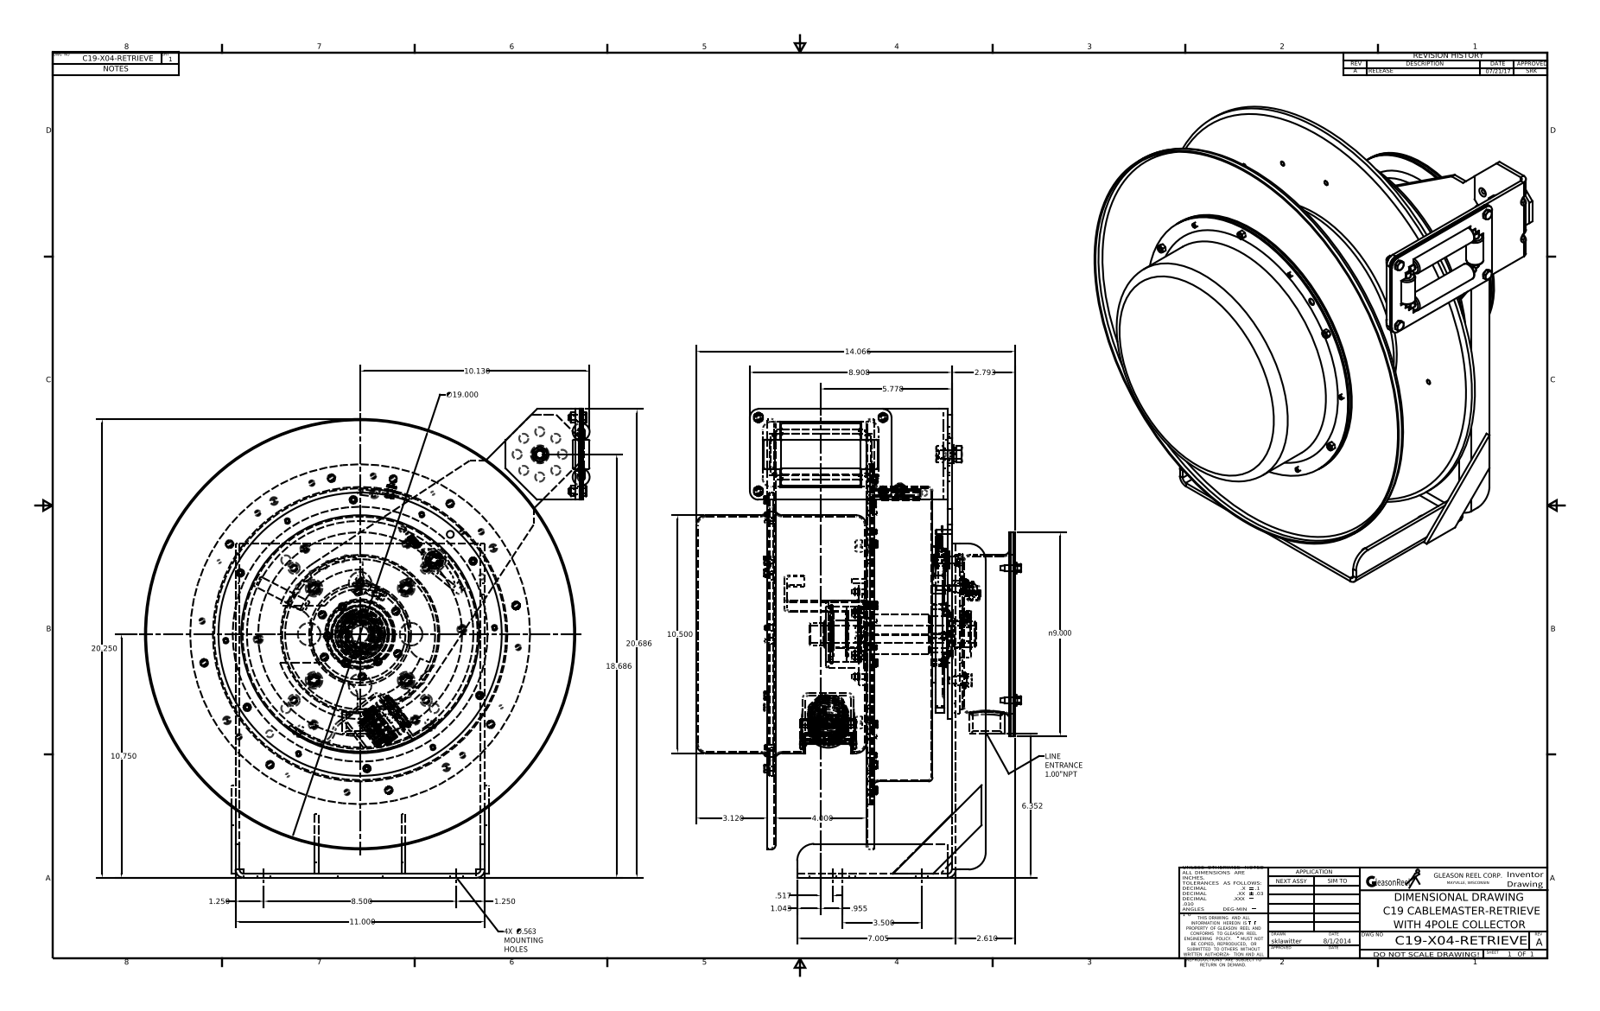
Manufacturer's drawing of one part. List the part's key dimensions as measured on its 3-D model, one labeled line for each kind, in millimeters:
Part name (STEP PRODUCT): C19-X04-RETRIEVE (SW)
STEP written by: Autodesk Inventor 2016 (AUTOMOTIVE_DESIGN)
Units: millimetres
Bodies: 173 solids, 3480 faces (1373 planar, 1017 cylindrical, 1090 other)
Overall size (bounding box): 525.44 × 498.61 × 363.98
Volume: 3 830 000 mm³ · Surface area: 3 140 000 mm²
Round holes (diameter × count): ⌀6.35 ×39, ⌀5 ×30, ⌀4.13 ×26, ⌀5.56 ×14, ⌀10.31 ×13, ⌀5.69 ×12, ⌀10.72 ×12, ⌀3.96 ×7, ⌀7.14 ×7, ⌀5.05 ×6, ⌀5.36 ×6, ⌀25.4 ×6
Round bosses / shafts (diameter × count): ⌀5 ×30, ⌀6 ×10, ⌀10.29 ×6, ⌀10 ×6, ⌀4.85 ×6, ⌀12.7 ×5, ⌀11.6 ×5, ⌀8 ×5
Partial cylindrical surfaces — rounded edges, fillets, slot ends (radius × count): R0.76 ×67, R0.25 ×64, R0.38 ×39, R1.98 ×18, R0.15 ×12, R1.52 ×12, R3.15 ×8, R3.17 ×7
Main face-to-face distances: 1.52, 4.7, 4.55, 6.22, 3.18, 109.35, 104.65, 103.13, 68.26, 72.96
Hole centre spacings: 19.44, 25.4, 35.92, 46.93, 103.2, 138.26, 138.32, 31.75
